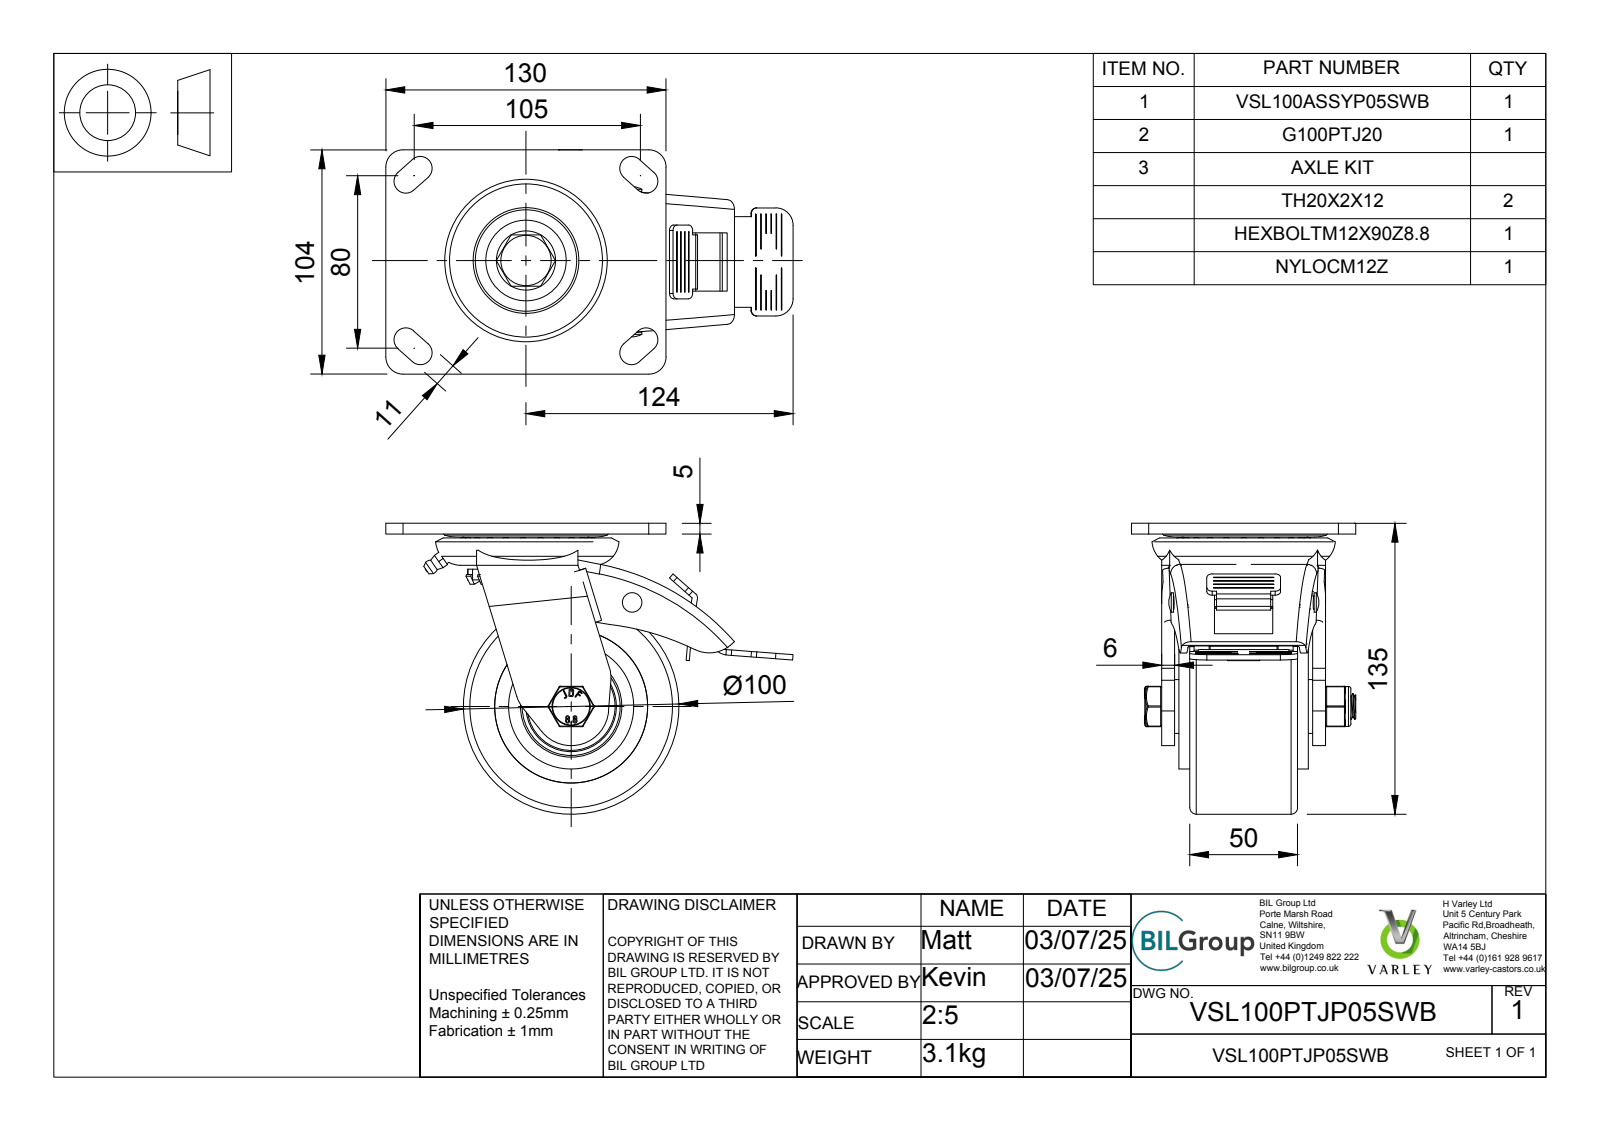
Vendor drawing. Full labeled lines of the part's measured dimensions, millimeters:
Part name (STEP PRODUCT): VSL100PTJP05SWB v4; VSL100ASSYP05SWB - 64 v1; VSL100ASSYP05SWB; 8X2DABOPANG_S_7_2_1 (+8 more)
STEP written by: Autodesk Translation Framework v14.10.0.0 (AUTOMOTIVE_DESIGN)
Units: millimetres
Bodies: 91 solids, 1536 faces (681 planar, 327 cylindrical, 528 other)
Overall size (bounding box): 189 × 135 × 104.01
Volume: 570 562 mm³ · Surface area: 219 769 mm²
Round holes (diameter × count): ⌀14 ×2, ⌀6.5 ×1, ⌀7 ×1, ⌀12 ×1, ⌀12.2 ×1, ⌀13 ×1, ⌀16 ×1, ⌀16.2 ×1, ⌀16.3 ×1, ⌀20 ×1, ⌀21 ×1, ⌀28.5 ×1
Round bosses / shafts (diameter × count): ⌀6 ×2, ⌀100 ×1, ⌀58 ×1, ⌀40.8 ×1, ⌀31.3 ×1, ⌀27 ×1, ⌀25 ×1, ⌀19.8 ×1
Partial cylindrical surfaces — rounded edges, fillets, slot ends (radius × count): R2.5 ×20, R0.5 ×19, R5.5 ×8, R8 ×6, R1 ×5, R3 ×5, R4 ×5, R0.47 ×4
Main face-to-face distances: 5, 13, 7, 57, 6, 63, 70, 50, 46, 8
Hole centre spacings: 0.91, 55.91
